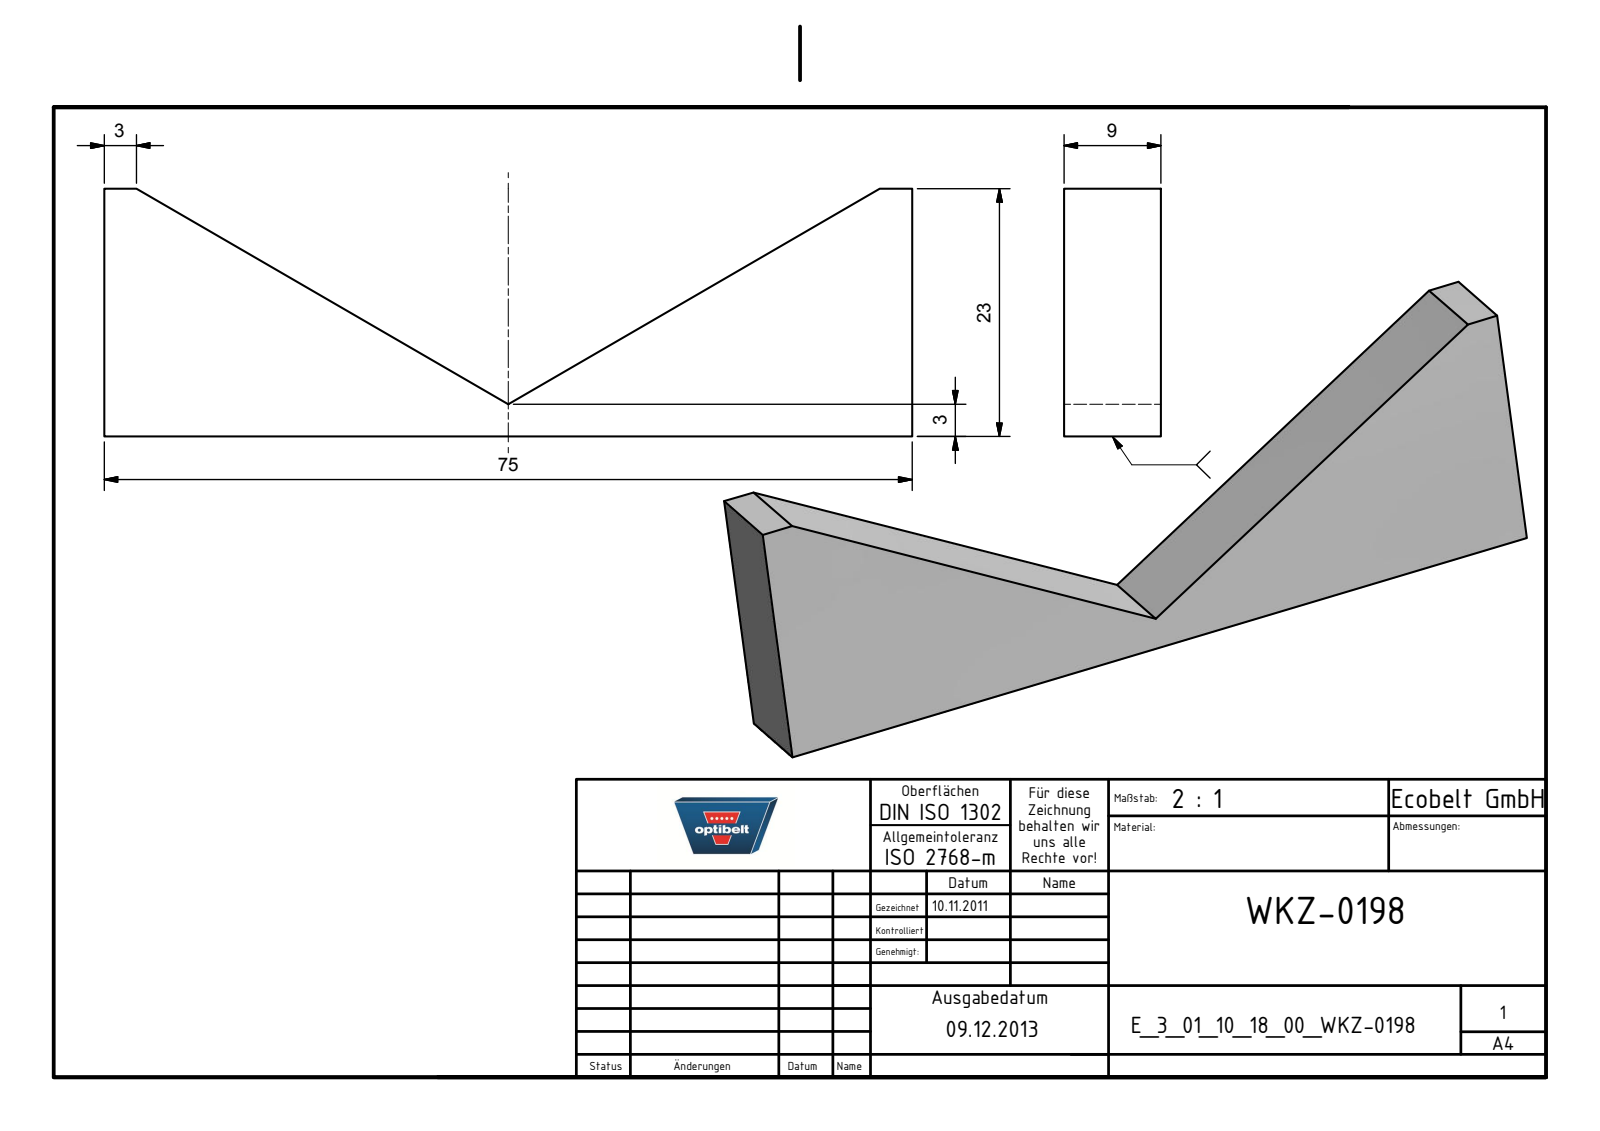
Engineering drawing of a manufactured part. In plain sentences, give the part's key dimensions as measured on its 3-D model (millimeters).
The part is named "E_3_01_10_18_00_WKZ-0198". Its 3-D file was written by "Autodesk Inventor 2025 (AUTOMOTIVE_DESIGN)". It is 1 solid with 9 faces: 9 planar, 0 cylindrical and 0 other. Overall it measures 75 by 23 by 9 millimeters. Its volume is 9 315 cubic millimeters and its surface area 3 931 square millimeters. The main face-to-face distances are 9, 75, 23.
